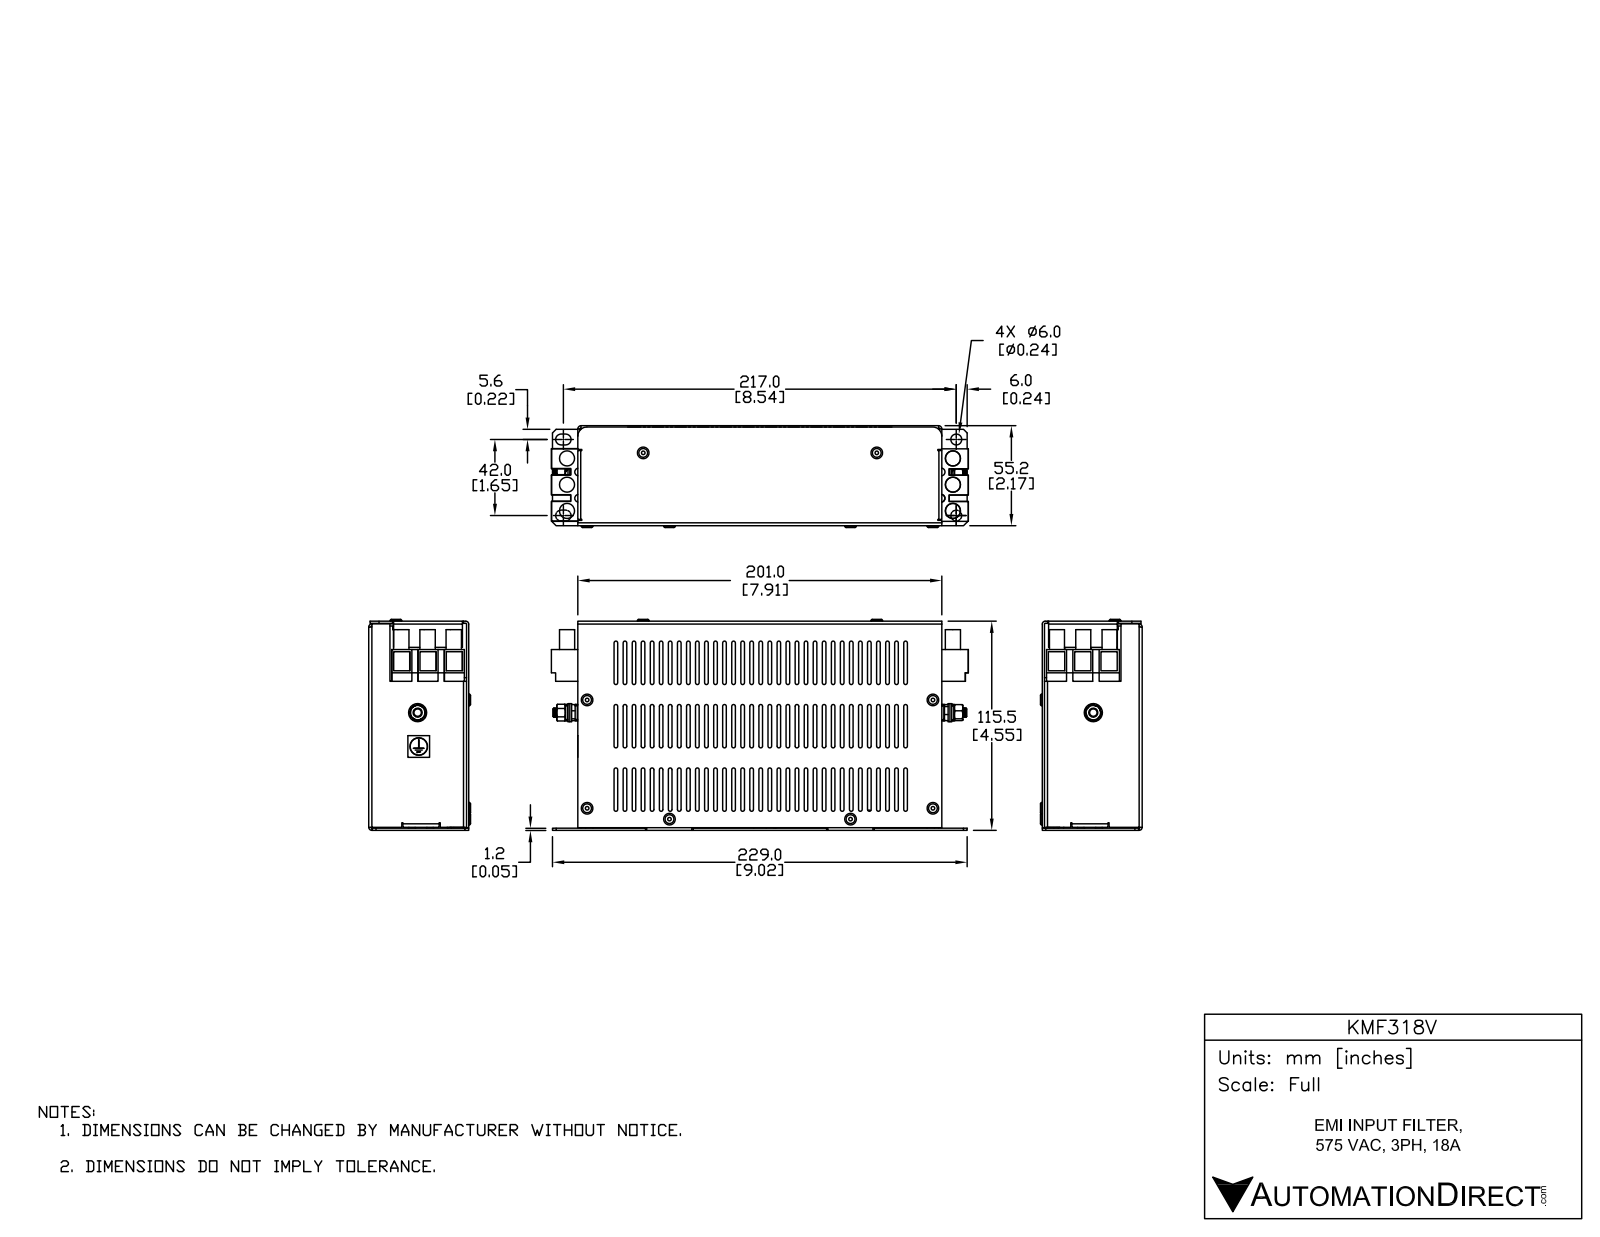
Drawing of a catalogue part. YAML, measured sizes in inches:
part_name: "KMF318V"
step_written_by: "SolidWorks 2017 (AUTOMOTIVE_DESIGN)"
units: inches
bodies: {solids: 38, faces: 2428, planar: 1384, cylindrical: 704, other: 340}
overall_size: [9.067, 4.587, 2.213]
volume: 10.46
surface_area: 324.9
round_holes:
  - {diameter: 0.079, count: 12}
  - {diameter: 0.138, count: 12}
  - {diameter: 0.13, count: 8}
  - {diameter: 0.169, count: 8}
  - {diameter: 0.154, count: 2}
  - {diameter: 0.236, count: 2}
  - {diameter: 0.051, count: 1}
  - {diameter: 0.165, count: 1}
  - {diameter: 0.165, count: 1}
  - {diameter: 0.205, count: 1}
  - {diameter: 0.383, count: 1}
round_bosses_or_shafts:
  - {diameter: 0.327, count: 24}
  - {diameter: 0.138, count: 12}
  - {diameter: 0.252, count: 4}
  - {diameter: 0.394, count: 1}
  - {diameter: 0.373, count: 1}
  - {diameter: 0.315, count: 1}
  - {diameter: 0.307, count: 1}
  - {diameter: 0.268, count: 1}
partial_cylinders:
  - {radius: 0.039, count: 198}
  - {radius: 0.02, count: 18}
  - {radius: 0.076, count: 7}
  - {radius: 0.067, count: 6}
  - {radius: 0.118, count: 4}
  - {radius: 0.016, count: 3}
  - {radius: 0.029, count: 3}
  - {radius: 0.063, count: 3}
face_to_face_distances: [0.047, 2.126, 2.079, 4.5, 2.173, 4.547, 4.453, 7.866, 0.571, 0.059]
hole_center_spacings: [0.394, 2.354, 0.571, 1.224, 1.389, 1.807, 3.15, 5.733]
